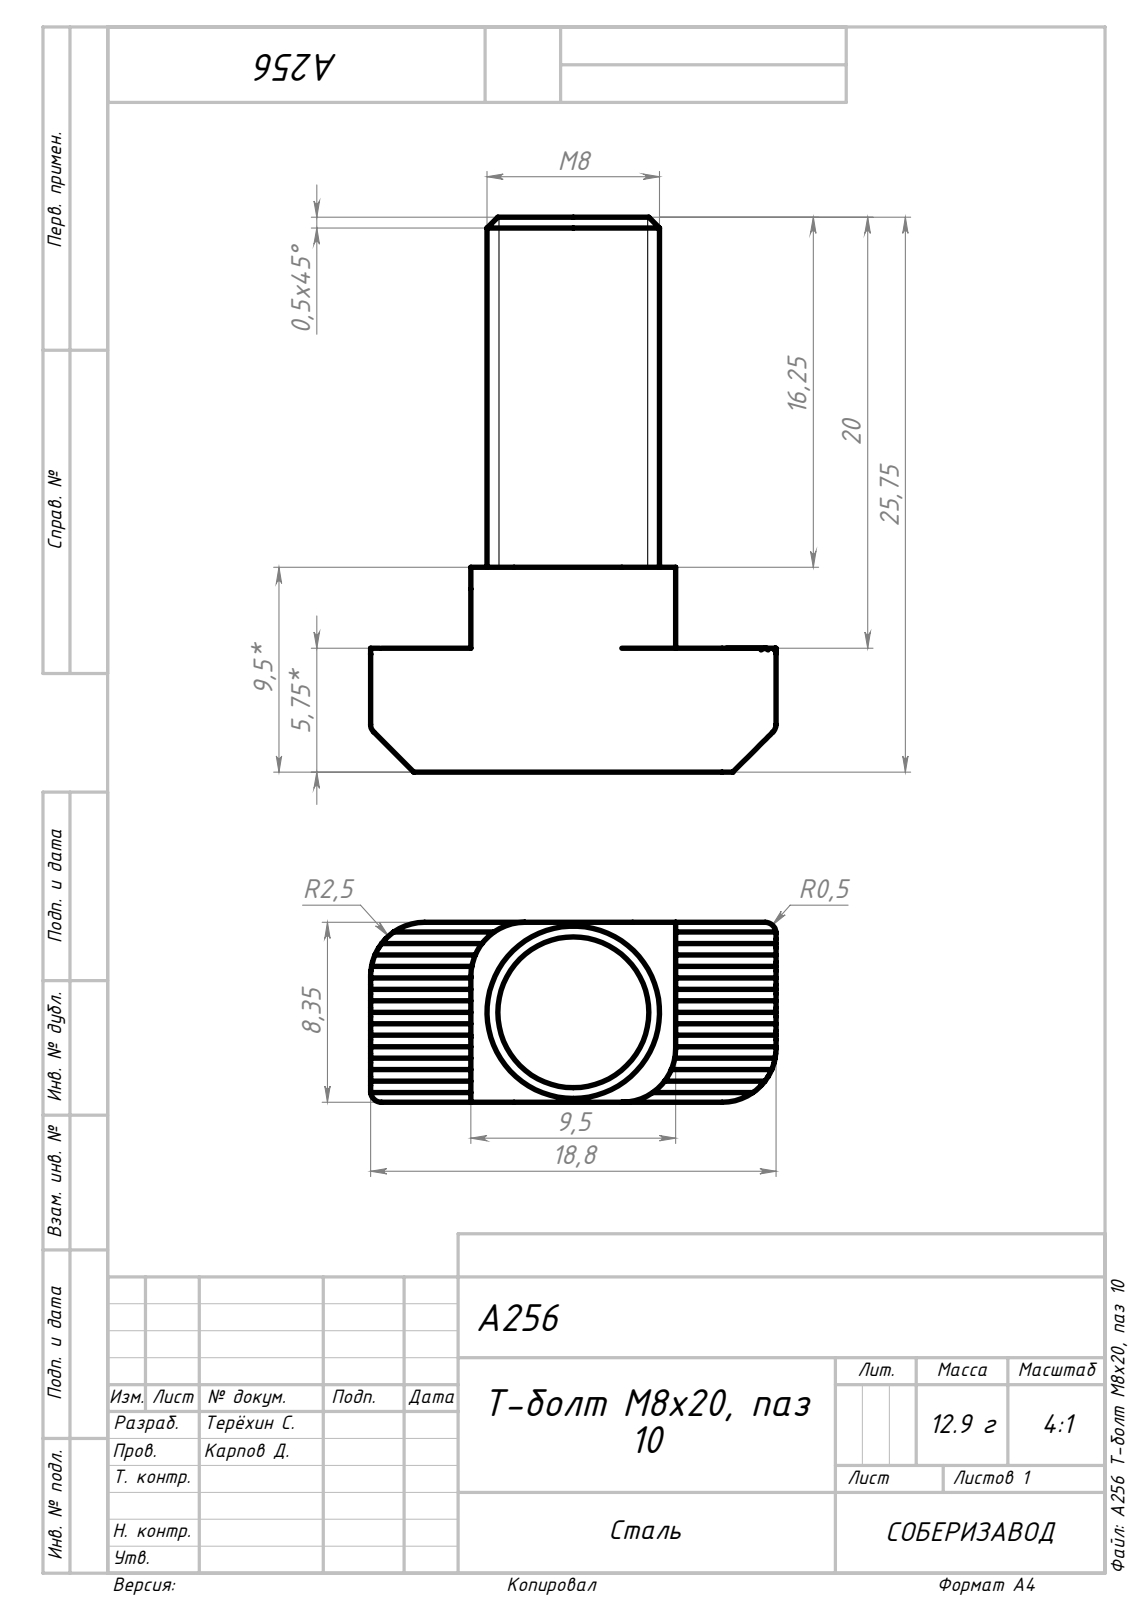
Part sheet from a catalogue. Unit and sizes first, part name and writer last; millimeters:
Units: millimetres
Overall size (bounding box): 25.75 × 18.8 × 8.35
Round bosses / shafts (diameter × count): ⌀8 ×1
Partial cylindrical surfaces — rounded edges, fillets, slot ends (radius × count): R0.5 ×22, R2.5 ×4
Main face-to-face distances: 8.34, 0.59, 1.18, 9.5, 25.75, 4.65, 14.15, 1.77, 2.36, 2.95
Volume: 1 944 mm³ · Surface area: 1 110 mm²
Bodies: 1 solid, 95 faces (45 planar, 42 cylindrical, 8 other)
Part name (STEP PRODUCT): А256 Т-болт М8х20, паз 10
STEP written by: SolidWorks 2021 (AUTOMOTIVE_DESIGN)
